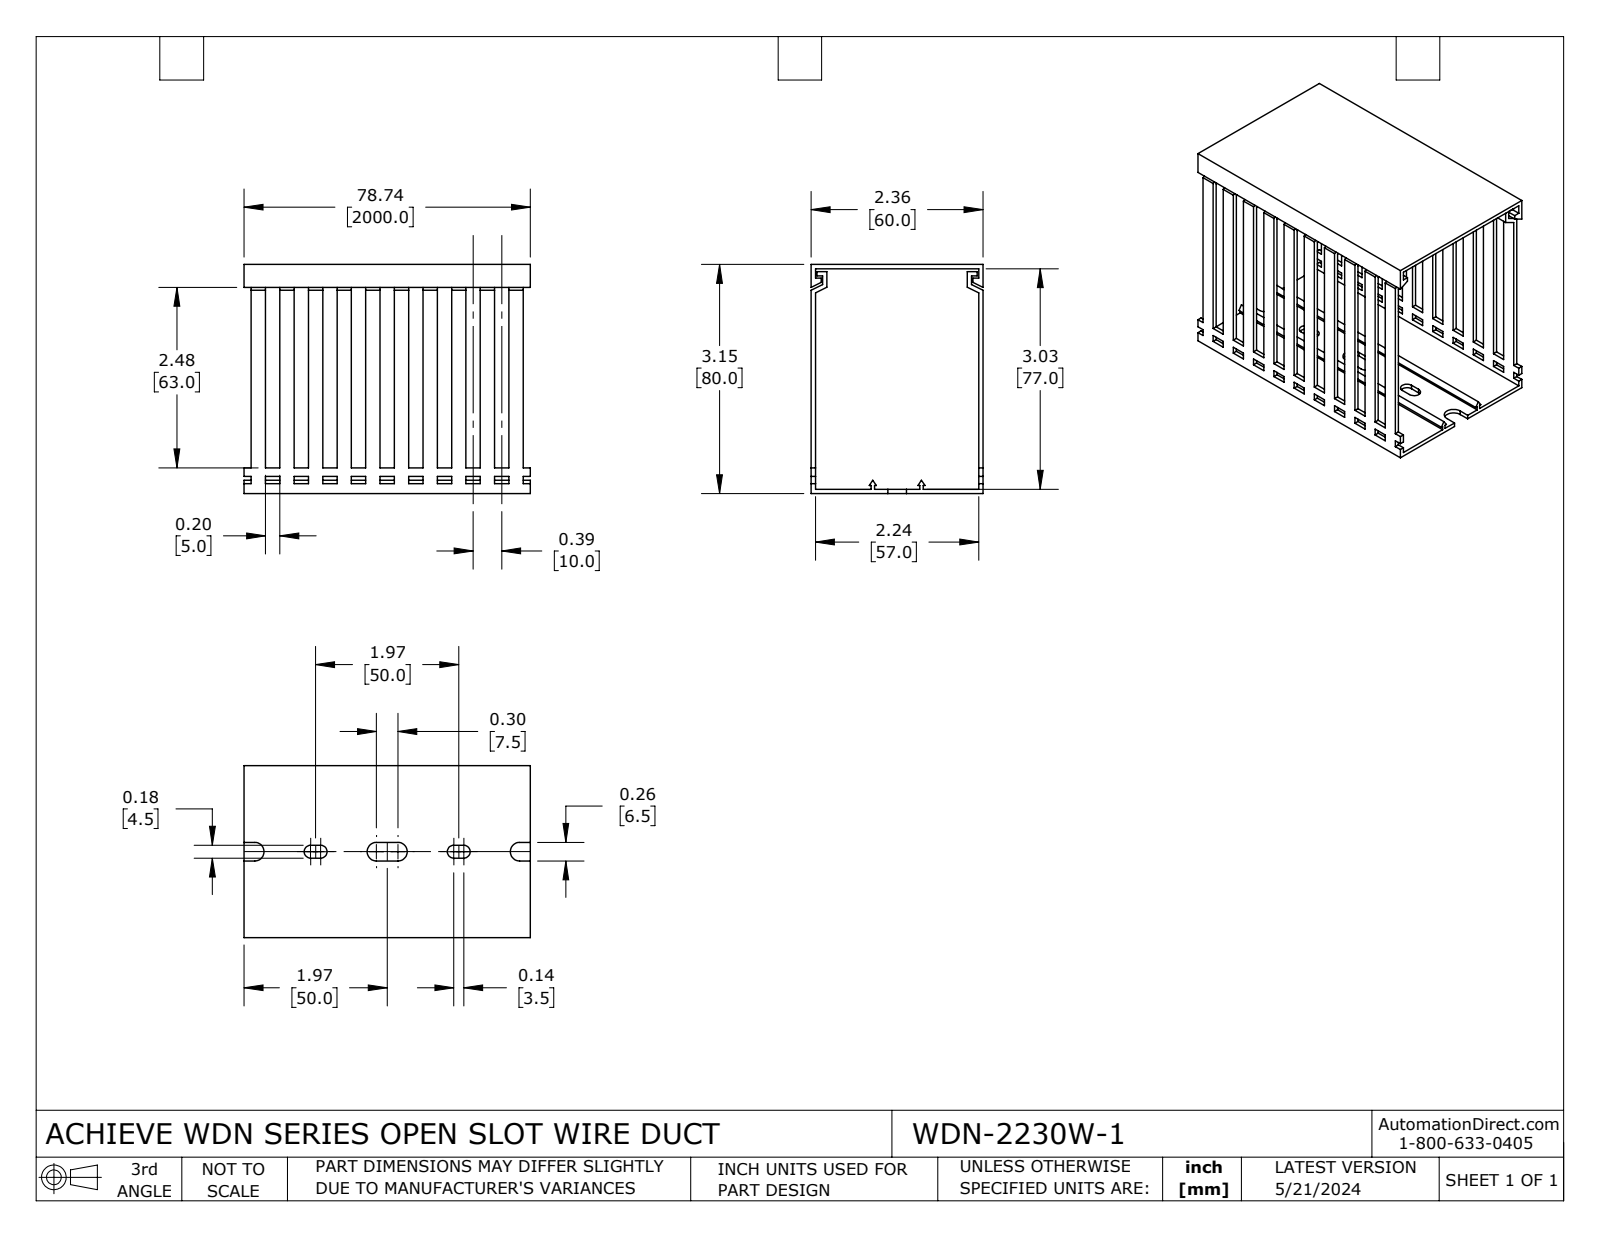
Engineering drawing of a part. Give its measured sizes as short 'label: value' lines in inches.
name: WDN-2230W-1
written by: SolidWorks 2023 (CONFIG_CONTROL_DESIGN)
unit: in
bodies: 2 solids, 350 faces (338 planar, 12 cylindrical, 0 other)
size: 3.937 × 3.15 × 2.362
volume: 2.068 in³; area: 79.42 in²
rounds: 4× R0.089, 4× R0.128
face distances: 0.059, 3.091, 2.303, 3.15, 2.362, 3.031, 0.197, 0.394, 2.244, 0.591
